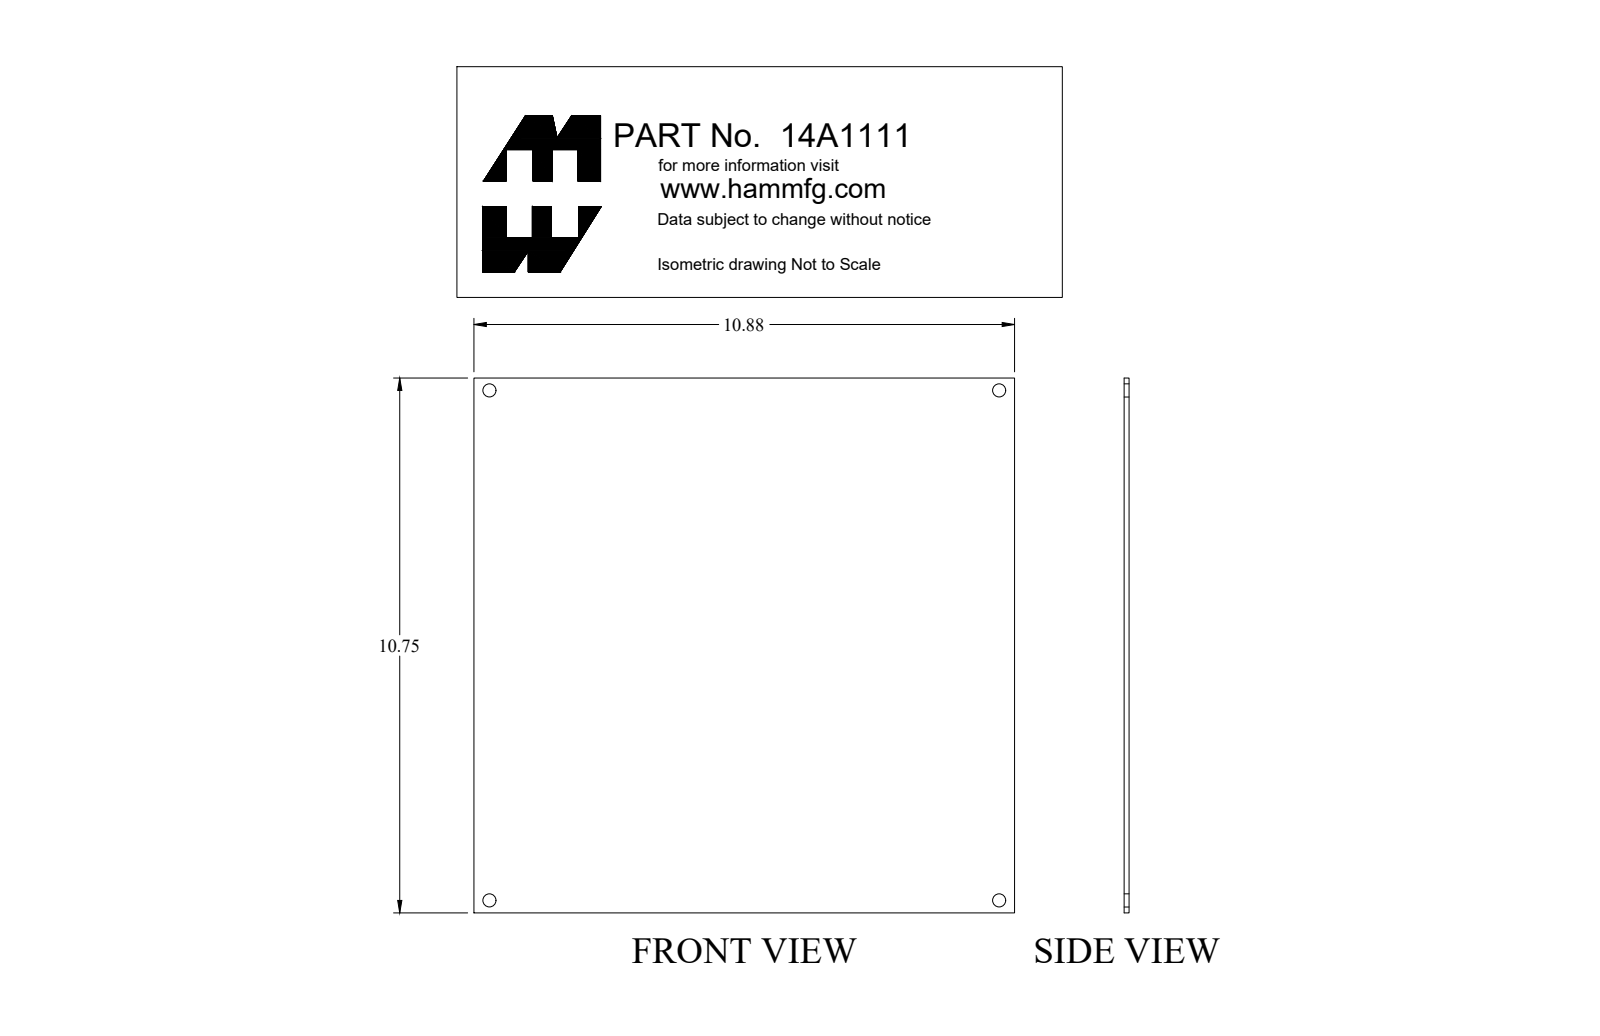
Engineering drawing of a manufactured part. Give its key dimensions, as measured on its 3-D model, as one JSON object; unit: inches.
{"part_name": "14A1111", "step_written_by": "SolidWorks 2018 (AUTOMOTIVE_DESIGN)", "units": "inches", "bodies": {"solids": 1, "faces": 10, "planar": 6, "cylindrical": 4, "other": 0}, "overall_size": [10.875, 10.75, 0.1], "volume_in3": 11.67, "surface_area_in2": 238, "round_holes": [[0.265, 4]], "face_to_face_distances": [0.1, 10.75, 10.875], "hole_center_spacings": [10.25, 10.251, 14.496]}
